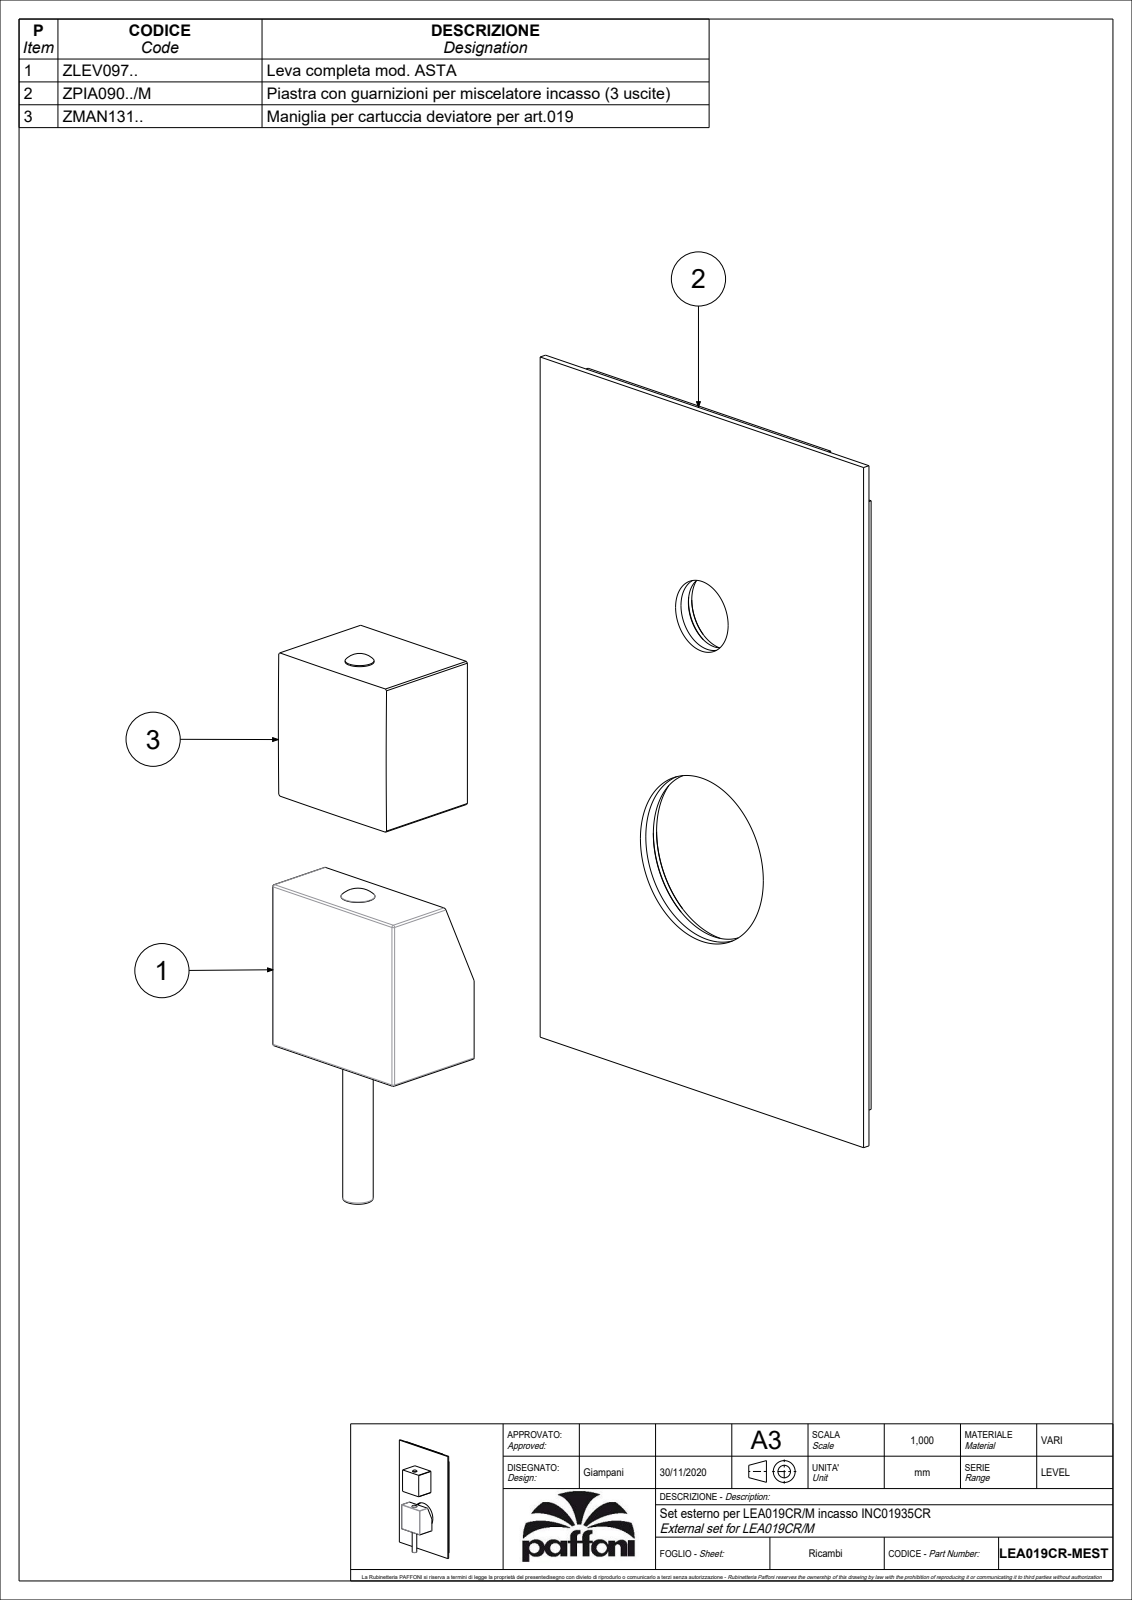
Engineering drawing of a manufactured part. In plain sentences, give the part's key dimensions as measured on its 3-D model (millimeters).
The part is named "LEA018CR-MEST". Its 3-D file was written by "CREO PARAMETRIC BY PTC INC, 2020044 (CONFIG_CONTROL_DESIGN)". It is 3 solids with 262 faces: 132 planar, 84 cylindrical and 46 other. Overall it measures 190 by 120 by 39.99 millimeters. Its volume is 94 737 cubic millimeters and its surface area 78 605 square millimeters. Round holes: 2 of diameter 5.5, 1 of diameter 3, 1 of diameter 3.2, 1 of diameter 4.2, 1 of diameter 6, 1 of diameter 8.1, 1 of diameter 14.8, 1 of diameter 19.5, 1 of diameter 21.5, 1 of diameter 25, 1 of diameter 36, 1 of diameter 45.6. Round bosses or shafts: 1 of diameter 54.6, 1 of diameter 28.5, 1 of diameter 8, 1 of diameter 7.6, 1 of diameter 5. Partial cylindrical surfaces (rounded edges, fillets, slot ends): 10 of radius 0.5, 1 of radius 28. The main face-to-face distances are 2, 0.8, 2.8, 40, 2.5, 42.5, 32, 34.8, 45, 34. The hole center spacings are 0.6, 10, 58, 68.
